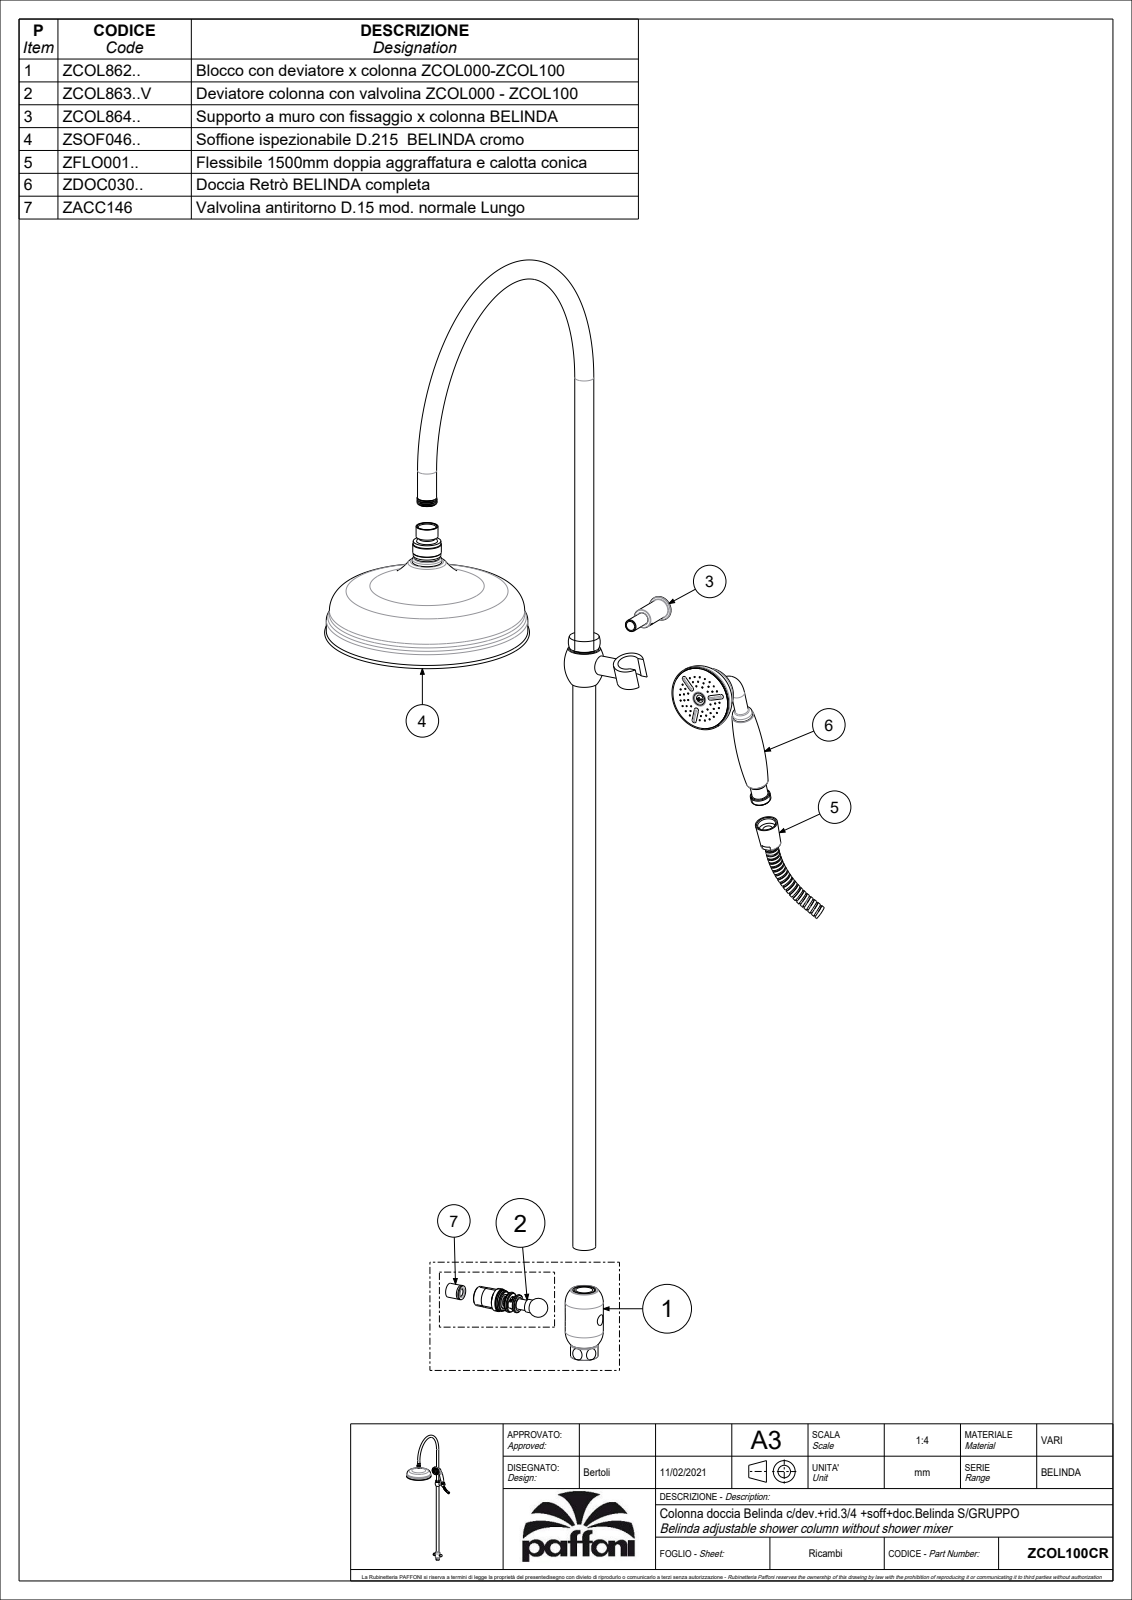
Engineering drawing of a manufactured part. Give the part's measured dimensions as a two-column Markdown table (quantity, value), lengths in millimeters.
| quantity | value |
| --- | --- |
| part name | 4071700CR_A; 4071700CR_B; 2041955GR; 4071700CR_C (+8 more) |
| STEP written by | CREO PARAMETRIC BY PTC INC, 2020044 (CONFIG_CONTROL_DESIGN) |
| units | millimeters |
| bodies | 27 solids, 1771 faces (453 planar, 651 cylindrical, 667 other) |
| overall size | 1202.88 × 517.5 × 215 |
| volume | 1 636 000 mm³ |
| surface area | 409 052 mm² |
| round holes (diameter × count) | 2 × 100, 1.2 × 45, 3 × 4, 13 × 3, 19 × 3, 10 × 2, 10.5 × 2, 11 × 2, 12.2 × 2, 14.5 × 2, 4 × 1, 5 × 1 |
| round bosses / shafts (diameter × count) | 14 × 5, 21 × 4, 20 × 3, 13 × 3, 30 × 2, 28 × 2, 24 × 2, 21.5 × 2 |
| partial cylindrical surfaces (radius × count) | 0.5 × 14, 3.1 × 1, 5.25 × 1, 5.35 × 1, 6.75 × 1, 9.75 × 1, 15 × 1 |
| main face-to-face distances | 15, 12, 7, 70, 164.38, 179.38, 22.65, 141.73, 156.73, 10.65 |
| hole center spacings | 14, 24, 19, 57, 27.18, 35.31, 71, 24.25 |
